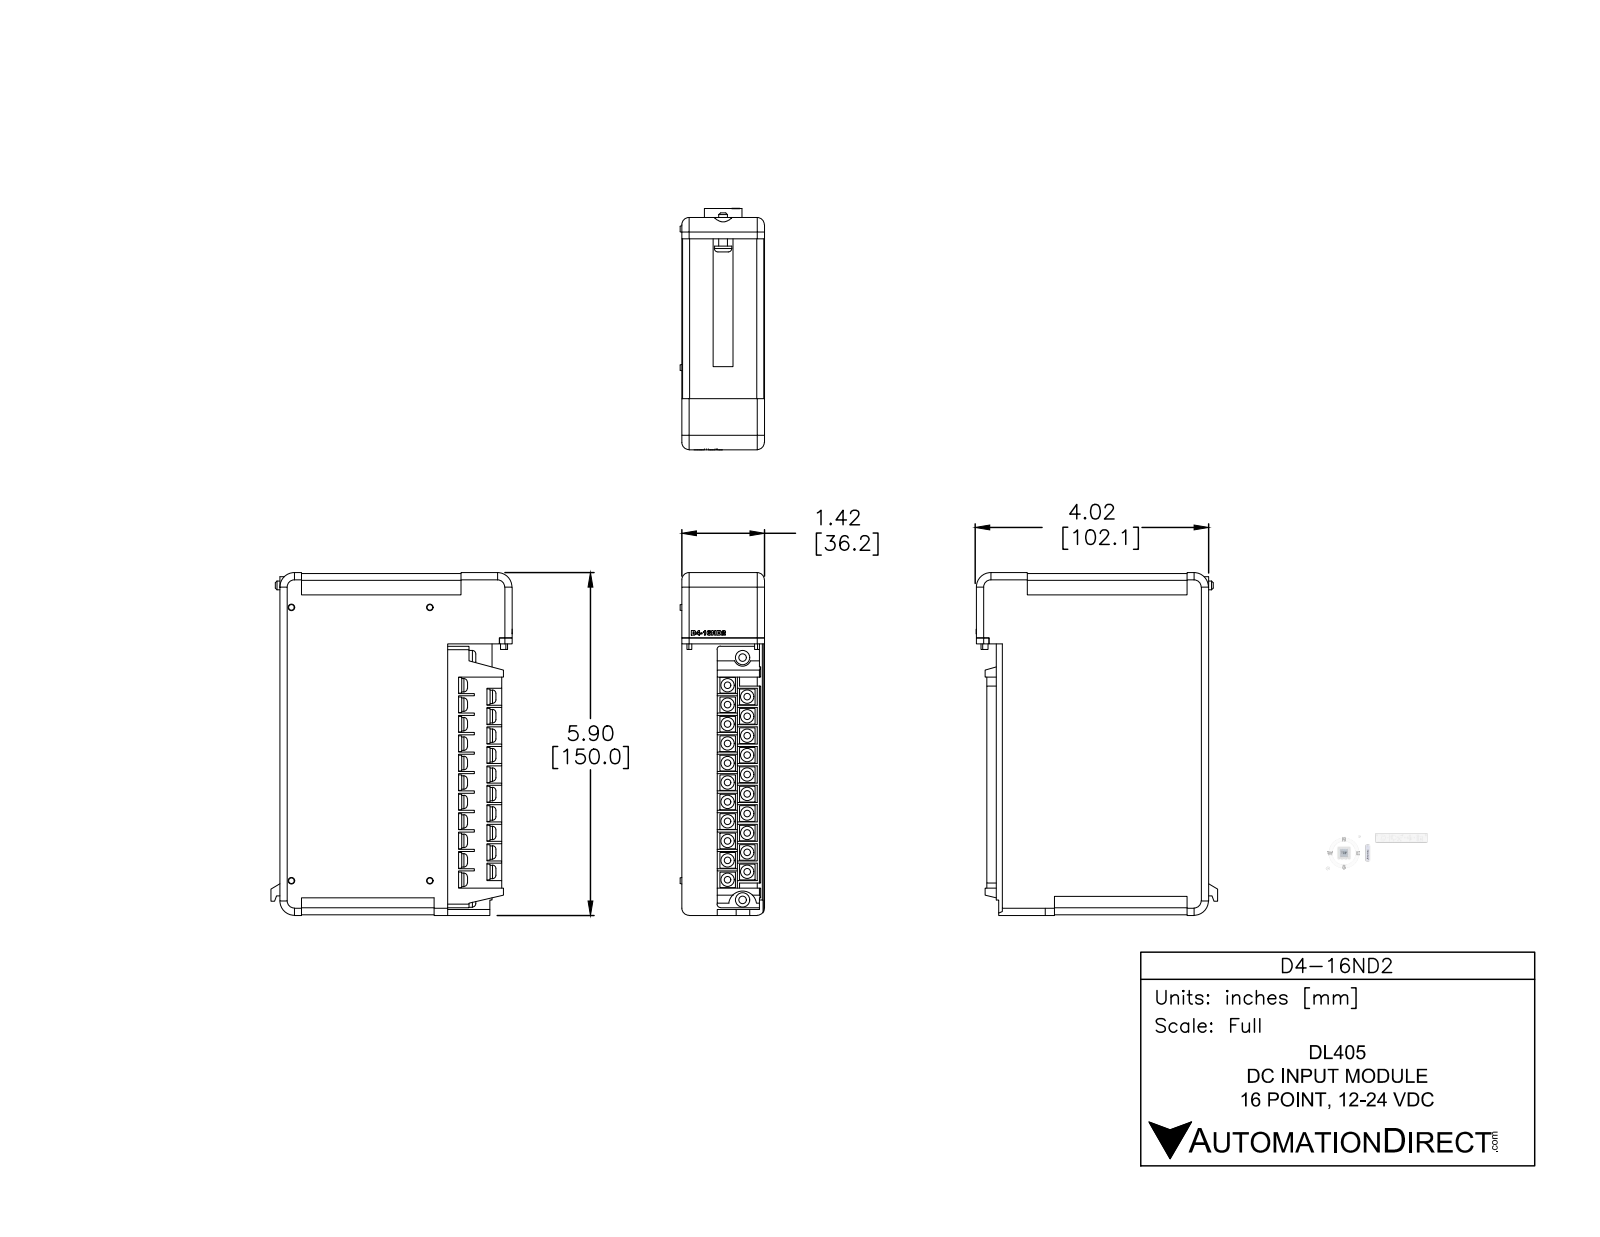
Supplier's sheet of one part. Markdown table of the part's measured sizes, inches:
| quantity | value |
| --- | --- |
| part name | D4-16ND2 |
| STEP written by | SolidWorks 2014 (AUTOMOTIVE_DESIGN) |
| units | inches |
| bodies | 14 solids, 605 faces (414 planar, 86 cylindrical, 105 other) |
| overall size | 5.905 × 4.156 × 1.455 |
| volume | 27.51 in³ |
| surface area | 86.83 in² |
| round bosses / shafts (diameter × count) | 0.23 × 21, 0.25 × 2, 0.3 × 1, 0.15 × 1 |
| partial cylindrical surfaces (radius × count) | 0.125 × 8, 0.12 × 4, 0.25 × 3, 0.015 × 2, 0.03 × 2, 0.06 × 2, 0.149 × 1, 0.151 × 1 |
| main face-to-face distances | 1.425, 0.015, 2.89, 5.875, 1.41, 0.47, 0.2, 0.955, 5.89, 1.21 |
